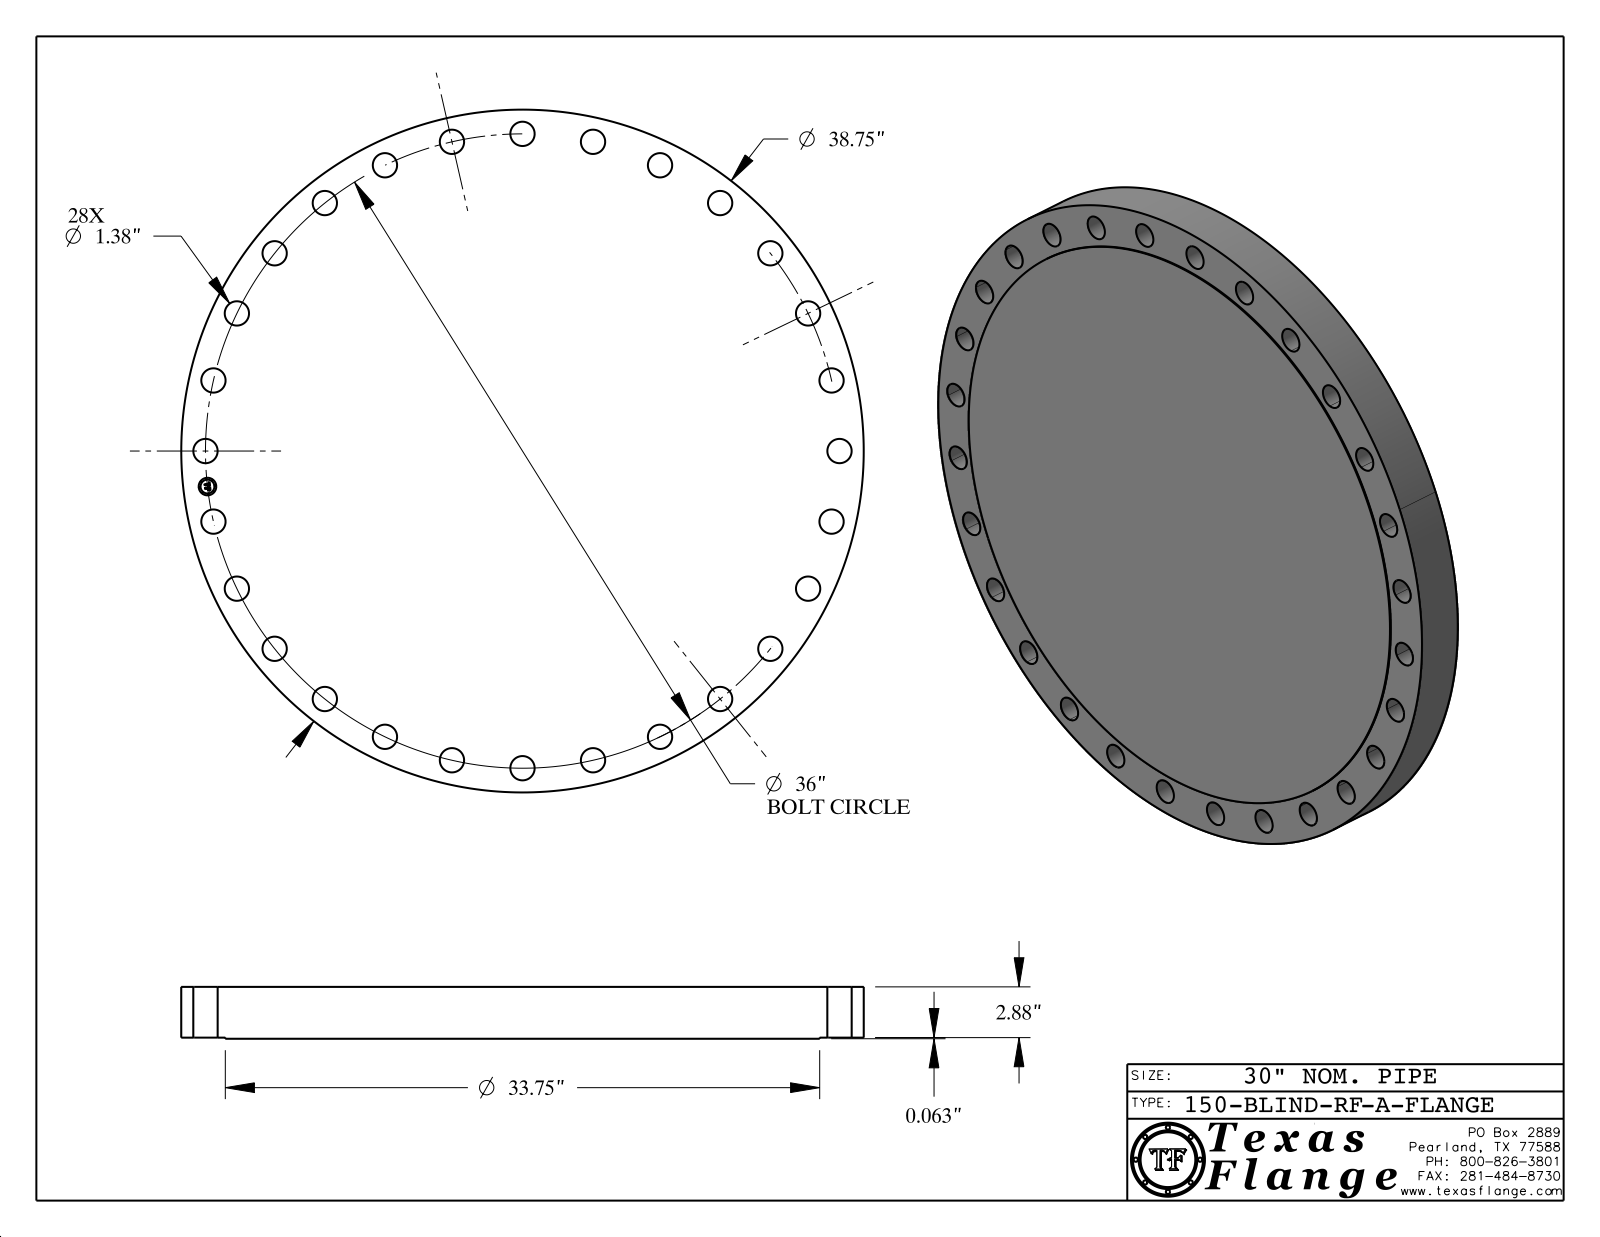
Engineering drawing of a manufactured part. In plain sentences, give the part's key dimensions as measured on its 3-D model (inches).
The part is named "150-BLIND-RF, Series A". Its 3-D file was written by "CATIA V5 STEP AP214 (AUTOMOTIVE_DESIGN)". It is 1 solid with 448 faces: 368 planar, 80 cylindrical and 0 other. Overall it measures 38.75 by 38.75 by 2.943 inches. Its volume is 3 332 cubic inches and its surface area 2 982 square inches. Round holes: 28 of diameter 1.38, 1 of diameter 1. Round bosses or shafts: 8 of diameter 0.061, 1 of diameter 38.75, 1 of diameter 33.75, 1 of diameter 0.788. The main face-to-face distances are 2.943, 0.063, 2.88, 0.015, 2.928, 2.865, 0.298, 0.293, 0.054, 0.193. The hole center spacings are 19.153, 4.031, 8.011, 11.89, 15.62, 22.446, 25.456, 32.435.
